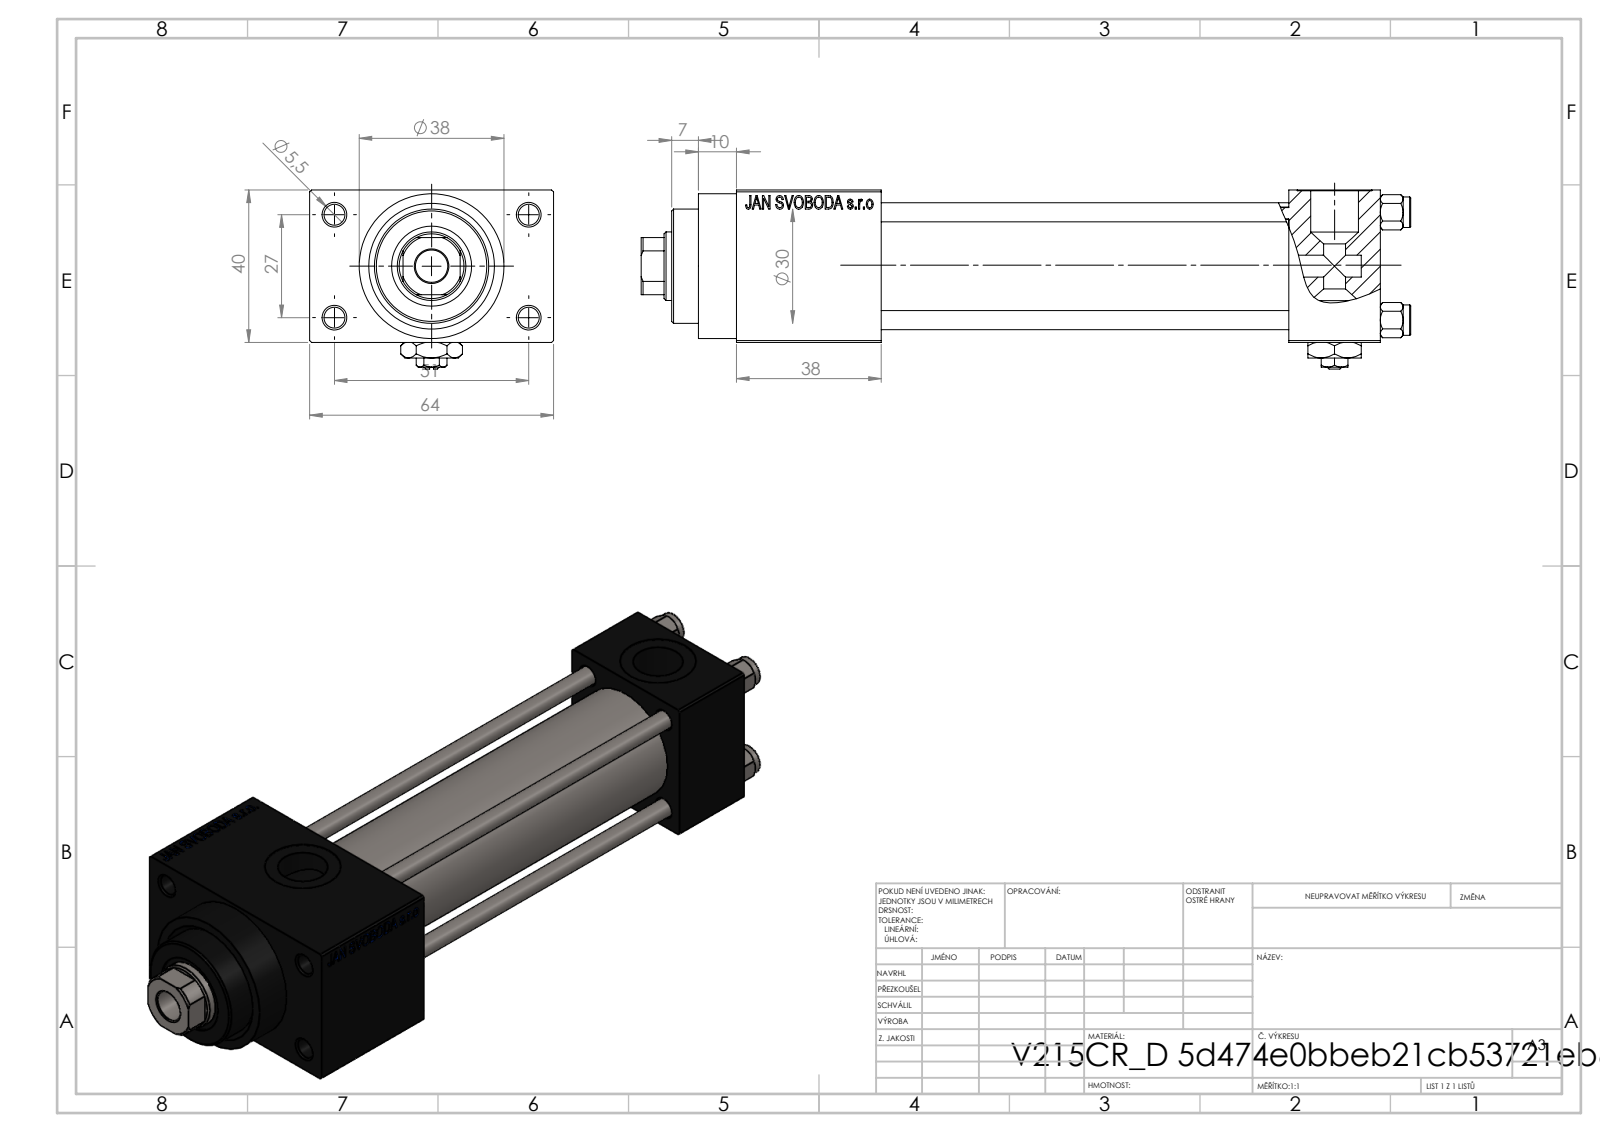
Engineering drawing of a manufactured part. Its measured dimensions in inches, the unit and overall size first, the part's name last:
Units: inches
Overall size (bounding box): 7.953 × 2.52 × 1.85
Round holes (diameter × count): ⌀0.197 ×4, ⌀0.217 ×4, ⌀0.787 ×3, ⌀0.276 ×2, ⌀0.518 ×2, ⌀0.335 ×1, ⌀0.709 ×1, ⌀0.827 ×1, ⌀0.984 ×1, ⌀1.181 ×1
Round bosses / shafts (diameter × count): ⌀0.315 ×4, ⌀1.496 ×1, ⌀1.22 ×1
Partial cylindrical surfaces — rounded edges, fillets, slot ends (radius × count): R0.335 ×1
Main face-to-face distances: 1.575, 0.472, 2.047, 4.213, 0.945, 5.157, 2.52, 1.496, 6.654, 5.709
Hole centre spacings: 0.448, 0.788, 1.114, 1.136, 1.177, 1.561, 1.903, 1.063
Volume: 13.15 in³ · Surface area: 128.6 in²
Bodies: 12 solids, 1154 faces (518 planar, 94 cylindrical, 542 other)
Part name (STEP PRODUCT): Zatka_pro_OIL_PORT; V215CR_D_Body; V215_VC_A; V215CR_VCP_D (+2 more)
STEP written by: SolidWorks 2019 (CONFIG_CONTROL_DESIGN)
